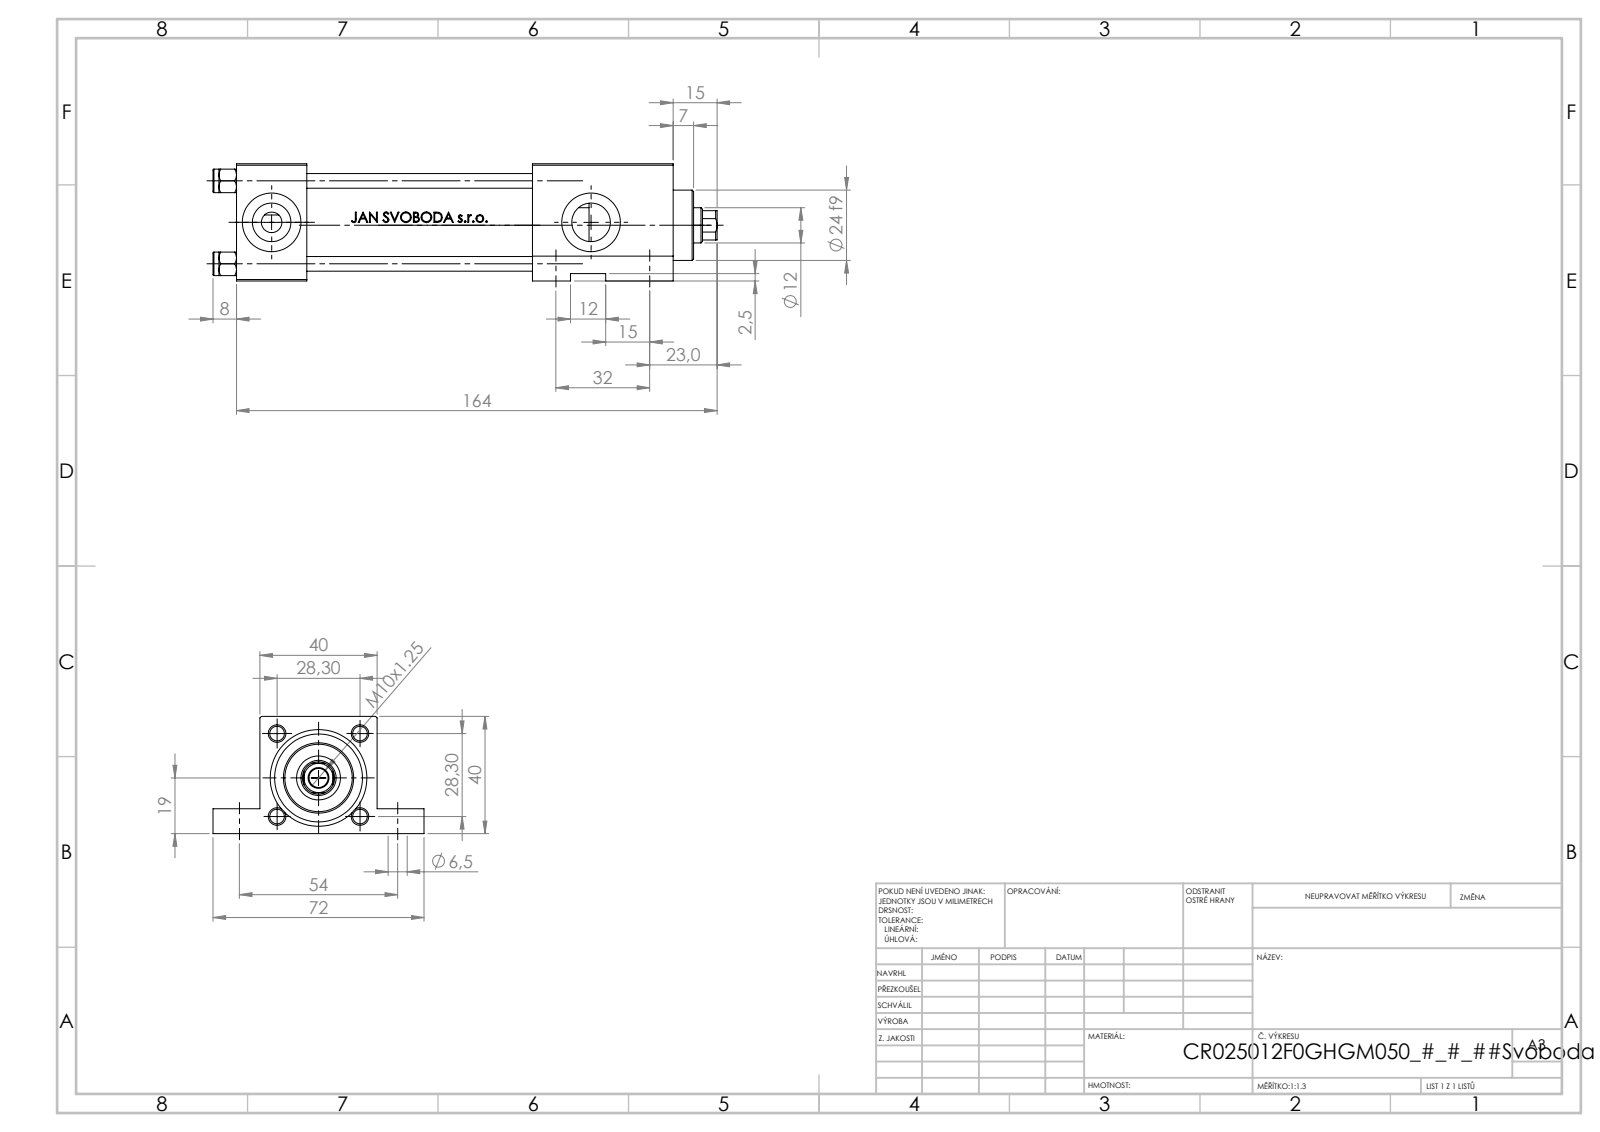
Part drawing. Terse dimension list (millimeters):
name: NUT_M5_F; V215CR_F_Body; V215CR_F_TYCINKA; V215_VC_A (+1 more)
written by: SolidWorks 2019 (CONFIG_CONTROL_DESIGN)
unit: mm
bodies: 11 solids, 1102 faces (436 planar, 126 cylindrical, 540 other)
size: 172 × 72 × 40
volume: 166 188 mm³; area: 66 738 mm²
holes: 5× ⌀6.5, 4× ⌀5, 3× ⌀20, 2× ⌀7, 2× ⌀13.16, 1× ⌀12, 1× ⌀15, 1× ⌀25, 1× ⌀30
bosses: 4× ⌀8, 1× ⌀31, 1× ⌀24
rounds: 1× R5.5
face distances: 40, 24, 8.5, 31.5, 48, 101, 77, 149, 125, 19.3
hole spacings: 28.3, 19.32, 20.73, 32, 40.02, 54, 62.77, 109
